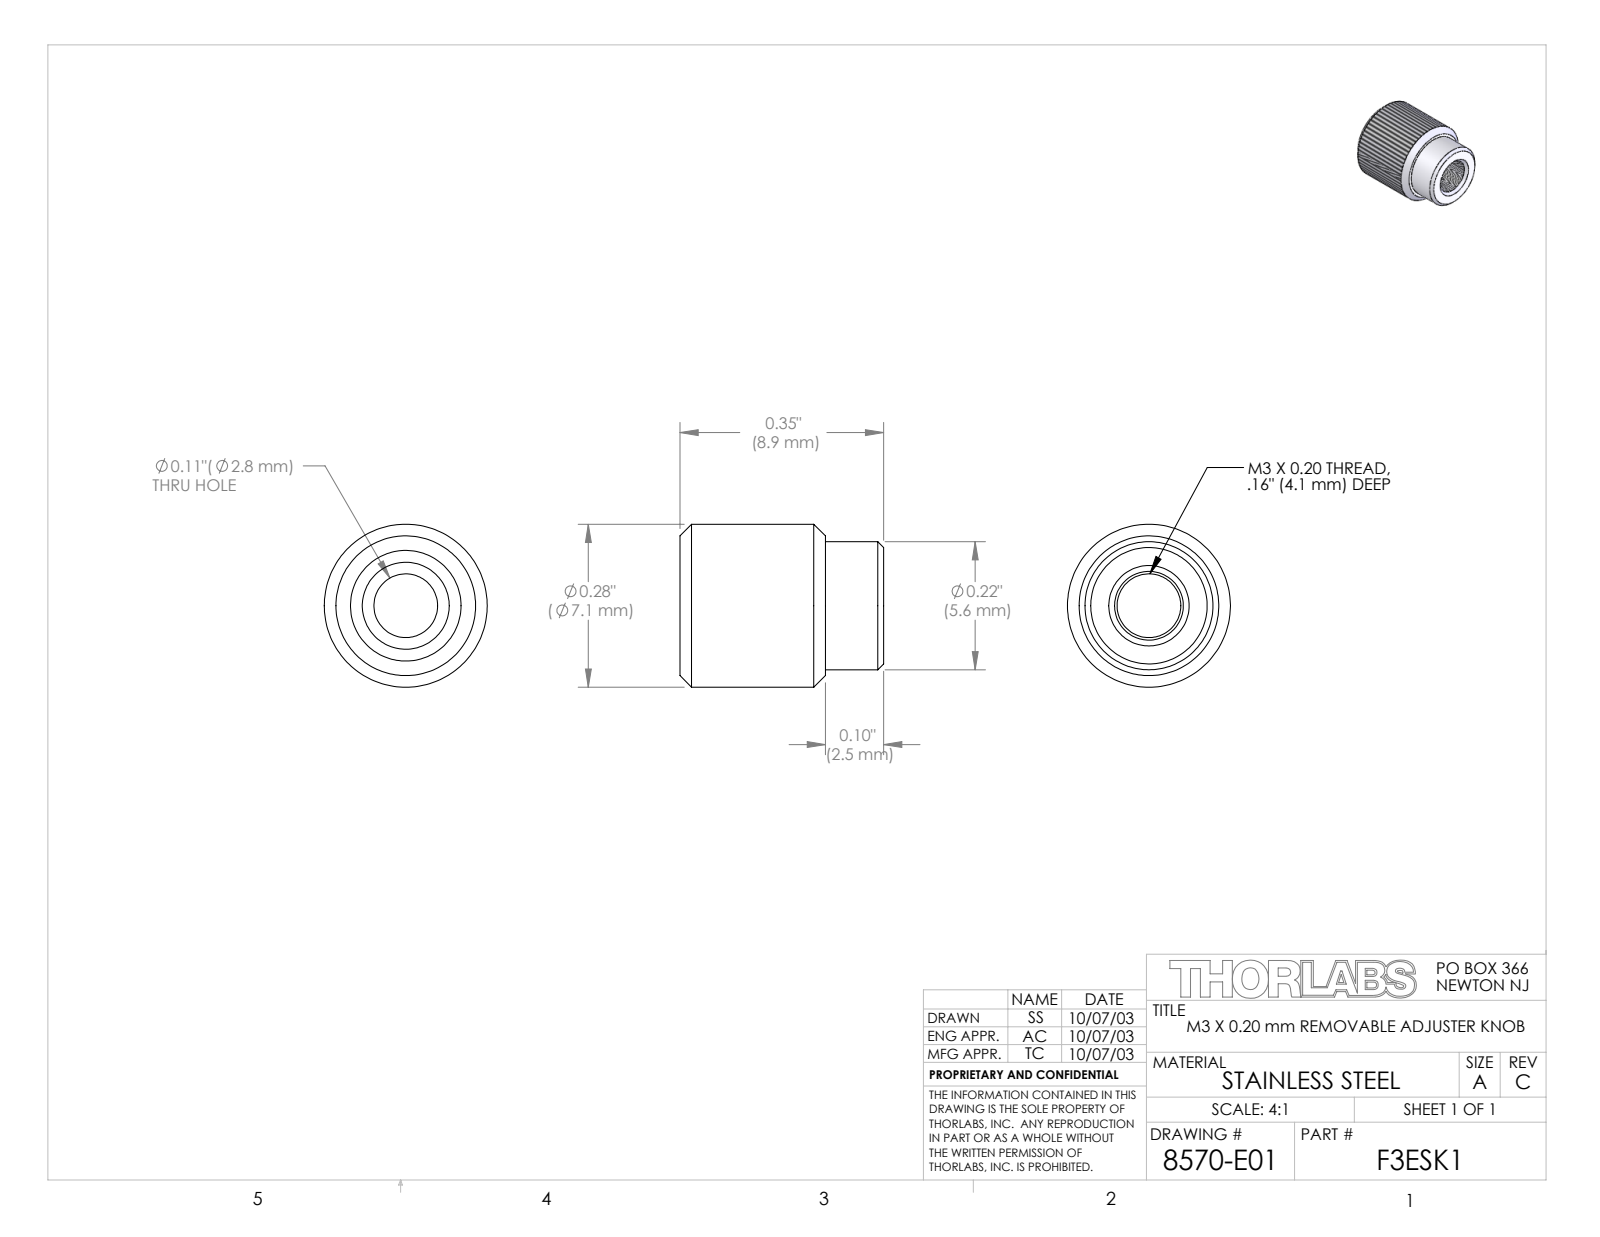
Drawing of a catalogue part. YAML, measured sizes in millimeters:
part_name: "8570-E0W"
step_written_by: "SolidWorks 2011 (AUTOMOTIVE_DESIGN)"
units: millimeters
bodies: {solids: 1, faces: 143, planar: 6, cylindrical: 129, other: 8}
overall_size: [8.9, 7.1, 7.1]
volume: 260
surface_area: 376
round_holes:
  - {diameter: 2.5, count: 1}
  - {diameter: 2.6, count: 1}
round_bosses_or_shafts:
  - {diameter: 7.1, count: 1}
  - {diameter: 5.6, count: 1}
  - {diameter: 2.6, count: 1}
face_to_face_distances: [8.9, 2.5, 6.4, 3.9, 1.4, 5]
